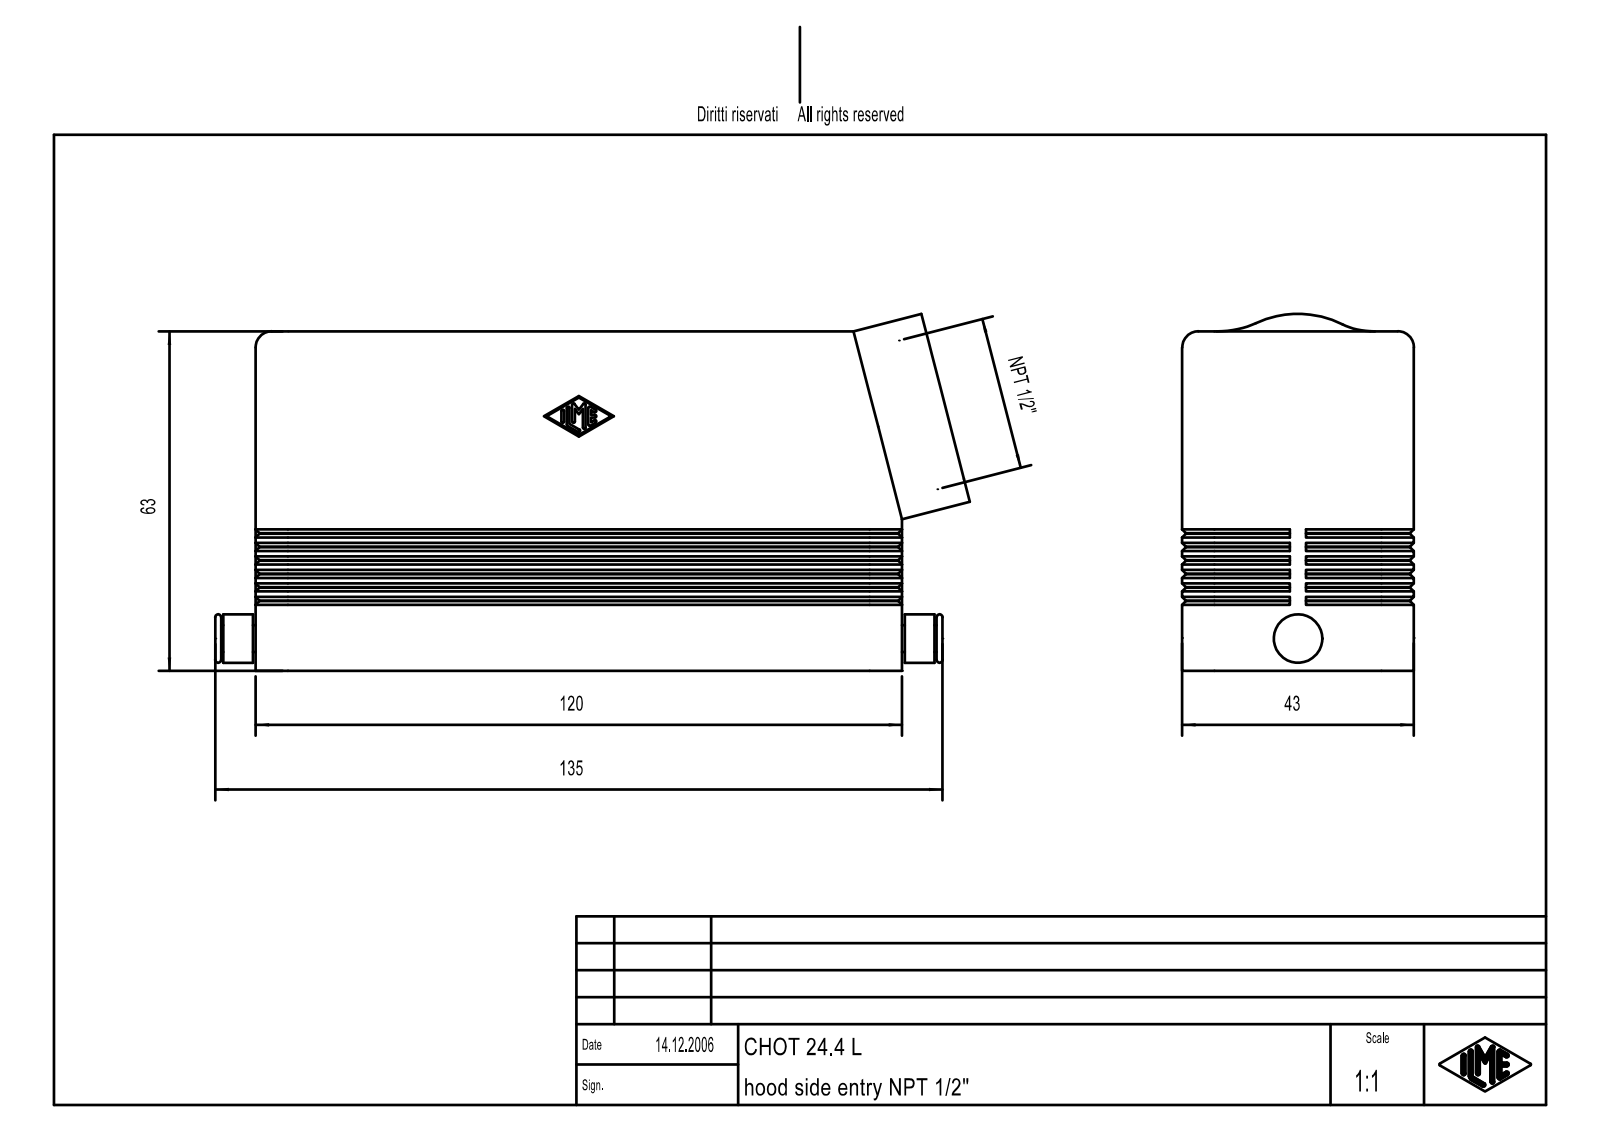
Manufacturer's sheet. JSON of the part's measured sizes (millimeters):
{"part_name": "MSBO8243", "step_written_by": "Creo Elements/Direct Modeling 18.0B 02-Dec-2011 (C) Parametric Technology GmbH (AUTOMOTIVE_DESIGN)", "units": "millimeters", "bodies": {"solids": 1, "faces": 415, "planar": 226, "cylindrical": 115, "other": 74}, "overall_size": [140.09, 66.25, 43], "volume_mm3": 93197, "surface_area_mm2": 51310, "round_holes": [[4, 4], [2.46, 3], [2.46, 1]], "round_bosses_or_shafts": [[27.45, 1], [9, 1], [5, 1]], "partial_cylinders_radius": [[0.25, 14], [3, 7], [2, 4], [5.3, 4], [6, 4], [1.5, 1], [12.39, 1]], "face_to_face_distances": [3, 40, 37, 43, 8.5, 11.5, 1.77, 5.3, 20, 105.5], "hole_center_spacings": [27, 104, 107.45]}
